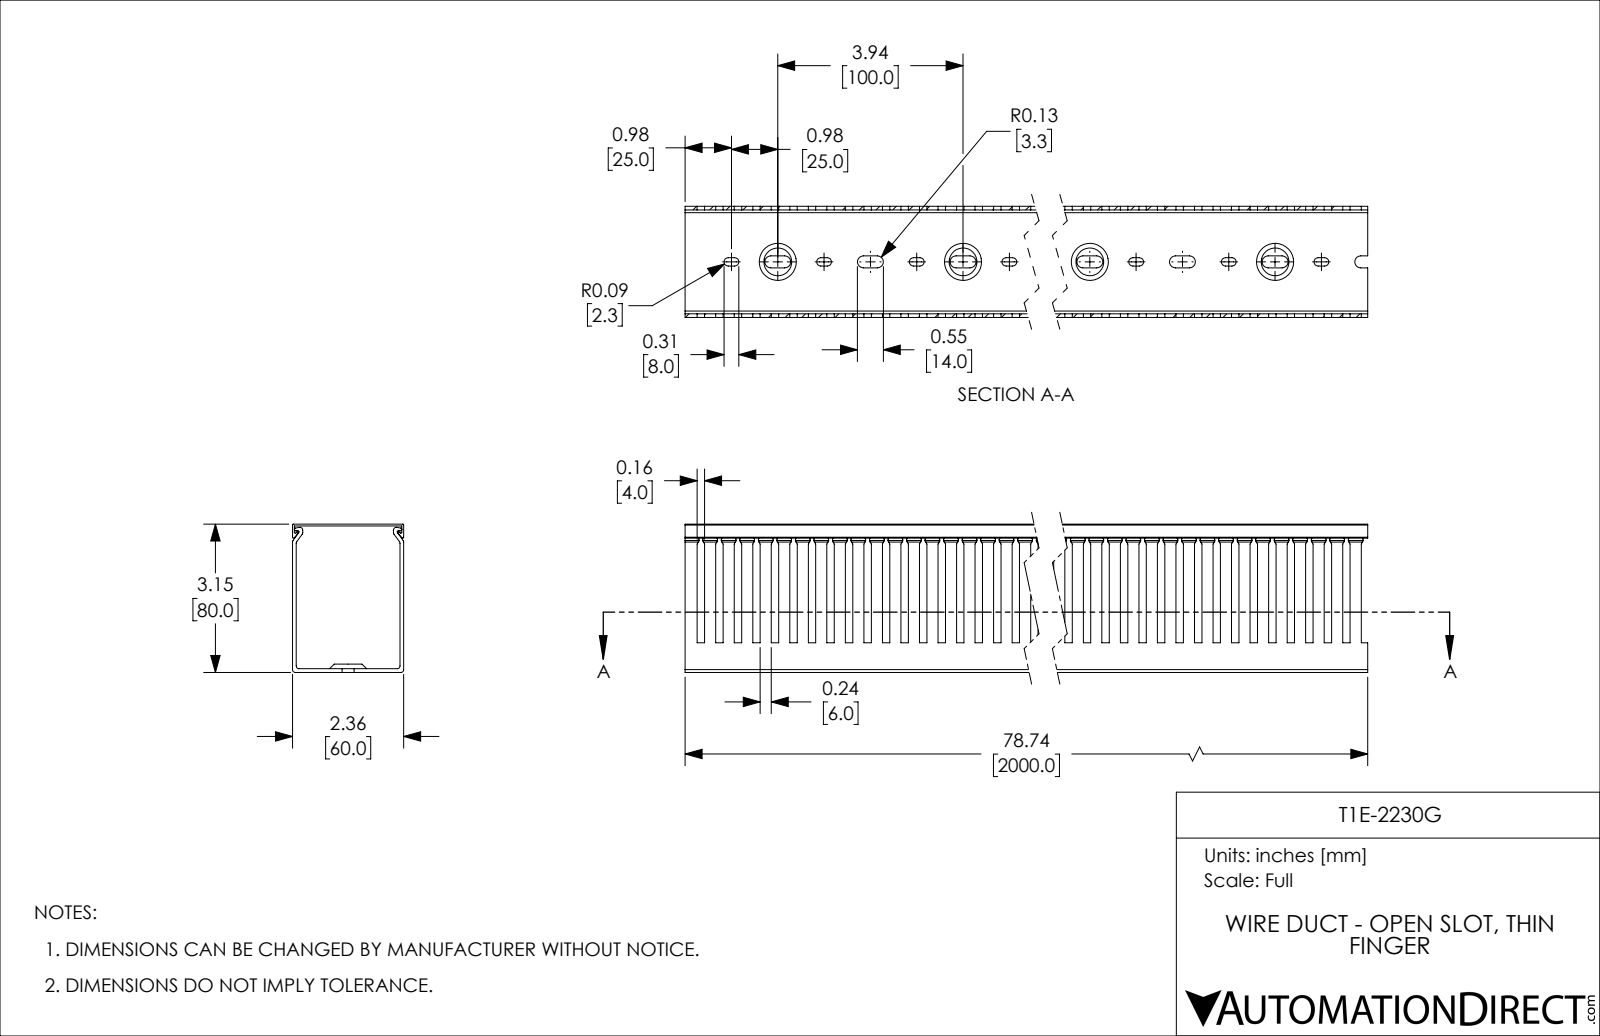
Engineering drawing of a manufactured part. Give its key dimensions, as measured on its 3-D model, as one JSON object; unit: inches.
{"part_name": "T1E-2230G-1", "step_written_by": "SolidWorks 2021 (CONFIG_CONTROL_DESIGN)", "units": "inches", "bodies": {"solids": 2, "faces": 1005, "planar": 534, "cylindrical": 431, "other": 40}, "overall_size": [78.74, 3.15, 2.362], "volume_in3": 62.24, "surface_area_in2": 1826, "partial_cylinders_radius": [[0.089, 80], [0.128, 80], [0.059, 12], [0.02, 8], [0.03, 6]], "face_to_face_distances": [0.079, 2.283, 2.362, 0.039, 2.205, 3.15, 3.11, 3.031, 3.071, 2.323]}
